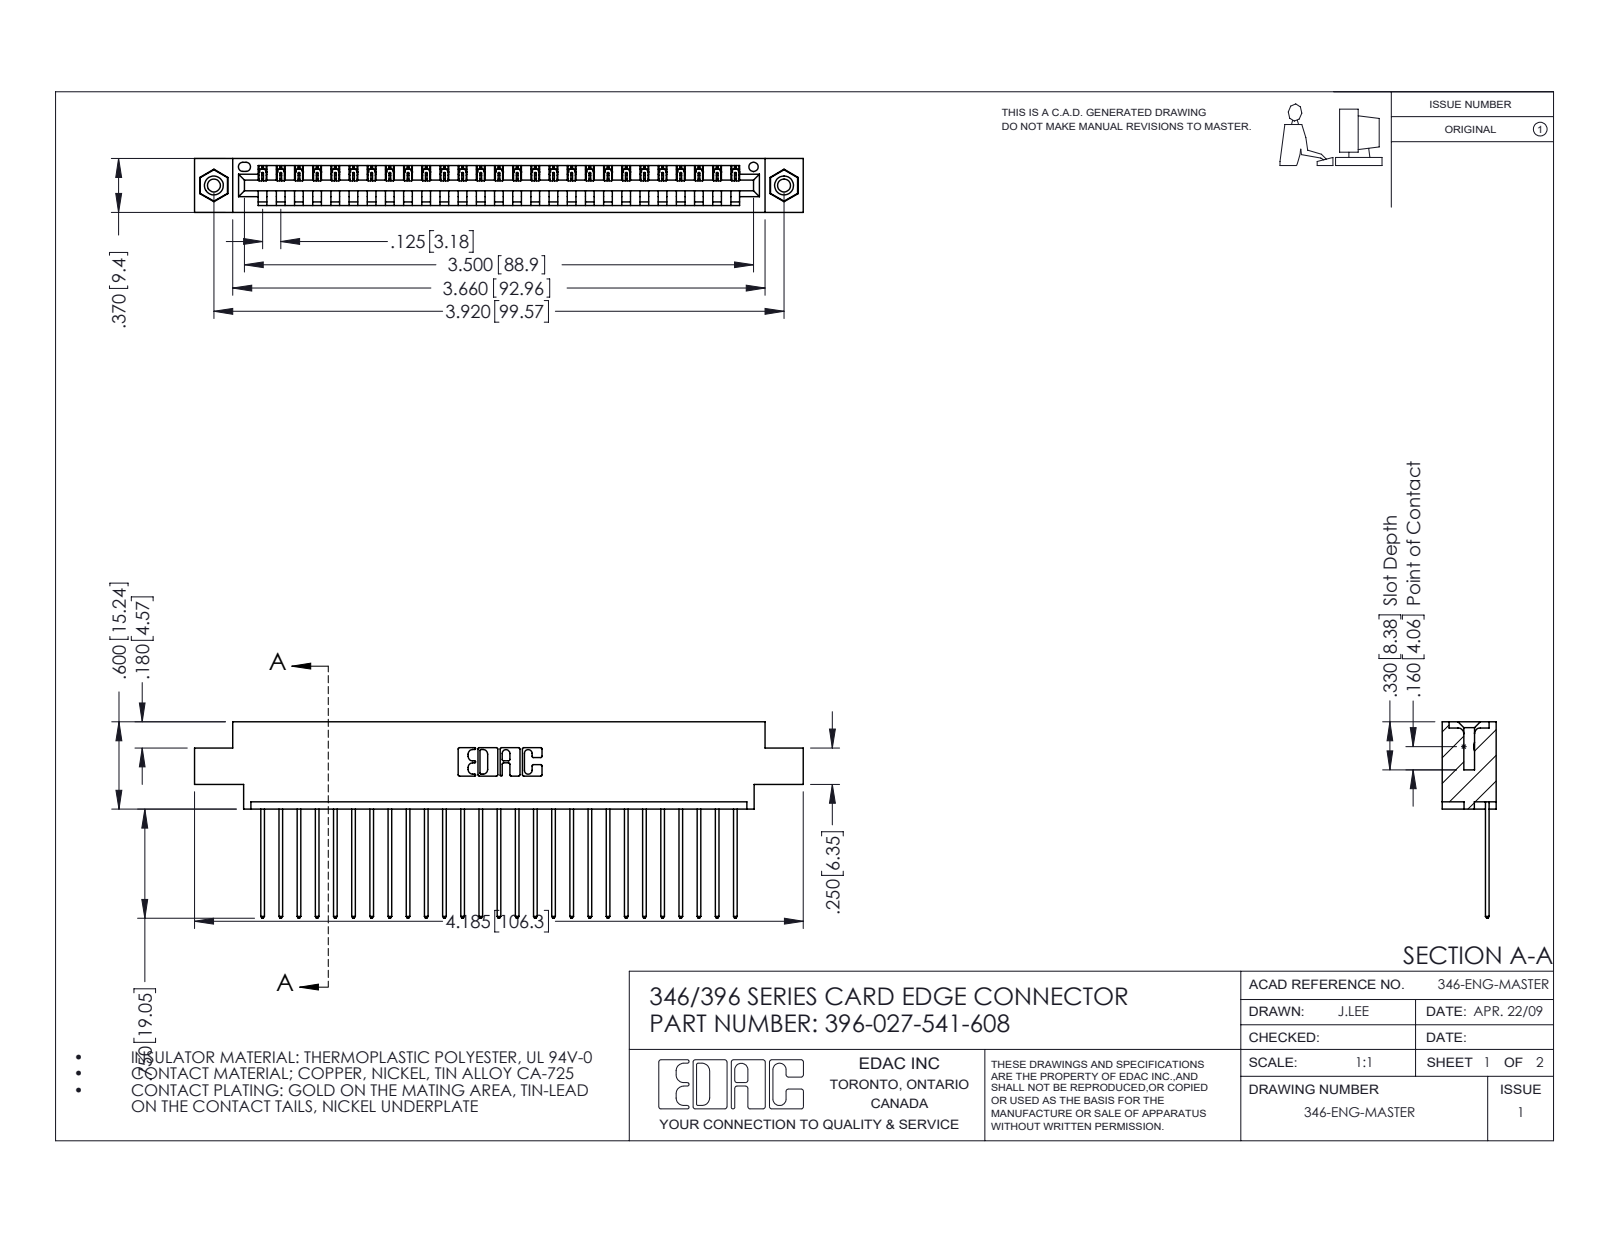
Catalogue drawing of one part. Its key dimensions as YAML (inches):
part_name: "345-292-001_345-293-141; 346 Part_0.170 Offset - 0.156 Dia-TI; 345-250-001_345-250-003-102; 396-027-541-608"
step_written_by: "SolidWorks 2016 (CONFIG_CONTROL_DESIGN)"
units: inches
bodies: {solids: 30, faces: 1752, planar: 1192, cylindrical: 544, other: 16}
overall_size: [4.185, 1.35, 0.37]
volume: 0.61
surface_area: 20.23
round_holes:
  - {diameter: 0.089, count: 2}
  - {diameter: 0.125, count: 2}
  - {diameter: 0.156, count: 2}
  - {diameter: 0.064, count: 1}
round_bosses_or_shafts:
  - {diameter: 0.155, count: 2}
partial_cylinders:
  - {radius: 0.006, count: 54}
  - {radius: 0.01, count: 54}
  - {radius: 0.01, count: 22}
  - {radius: 0.007, count: 6}
  - {radius: 0.031, count: 6}
  - {radius: 0.026, count: 3}
  - {radius: 0.031, count: 2}
  - {radius: 0.04, count: 2}
face_to_face_distances: [0.048, 0.322, 0.37, 0.25, 0.072, 0.298, 0.025, 0.222, 0.148, 0.1]
hole_center_spacings: [0.246, 3.712, 3.92]
